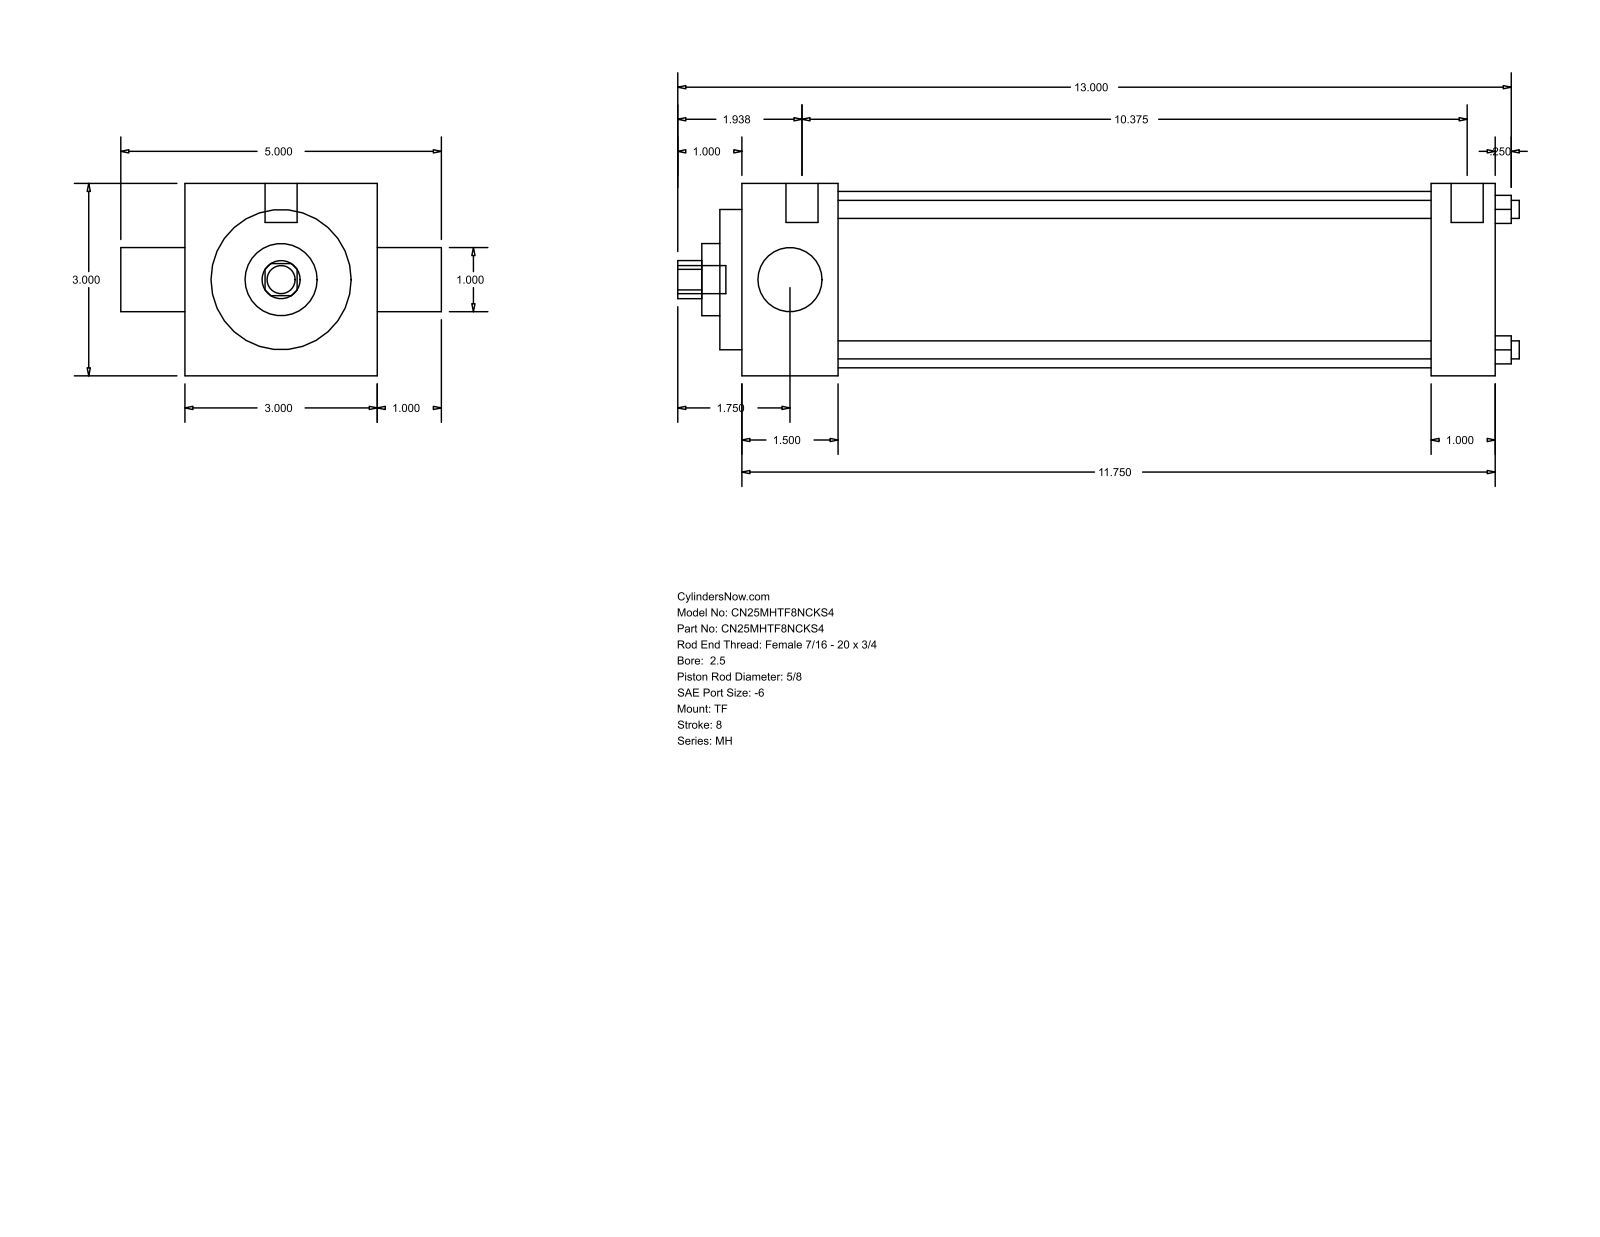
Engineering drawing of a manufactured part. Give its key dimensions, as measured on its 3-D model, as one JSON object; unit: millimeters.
{"part_name": "MH_TF__0250_0.625", "step_written_by": "GSSL Pune (CONFIG_CONTROL_DESIGN)", "units": "millimeters", "bodies": {"solids": 0, "faces": 86, "planar": 61, "cylindrical": 25, "other": 0}, "overall_size": [333.38, 127, 76.2], "round_holes": [[7.14, 4], [15.88, 1], [25.4, 1], [28.57, 1], [55.55, 1], [69.85, 1]], "round_bosses_or_shafts": [[5.56, 3], [12.7, 2], [11.11, 1]], "partial_cylinders_radius": [[7.54, 1]], "face_to_face_distances": [76.2, 298.45, 25.4, 38.1, 260.35, 273.05, 234.95, 8.73, 46.83, 281.78], "hole_center_spacings": [39.33, 55.62, 78.66]}
